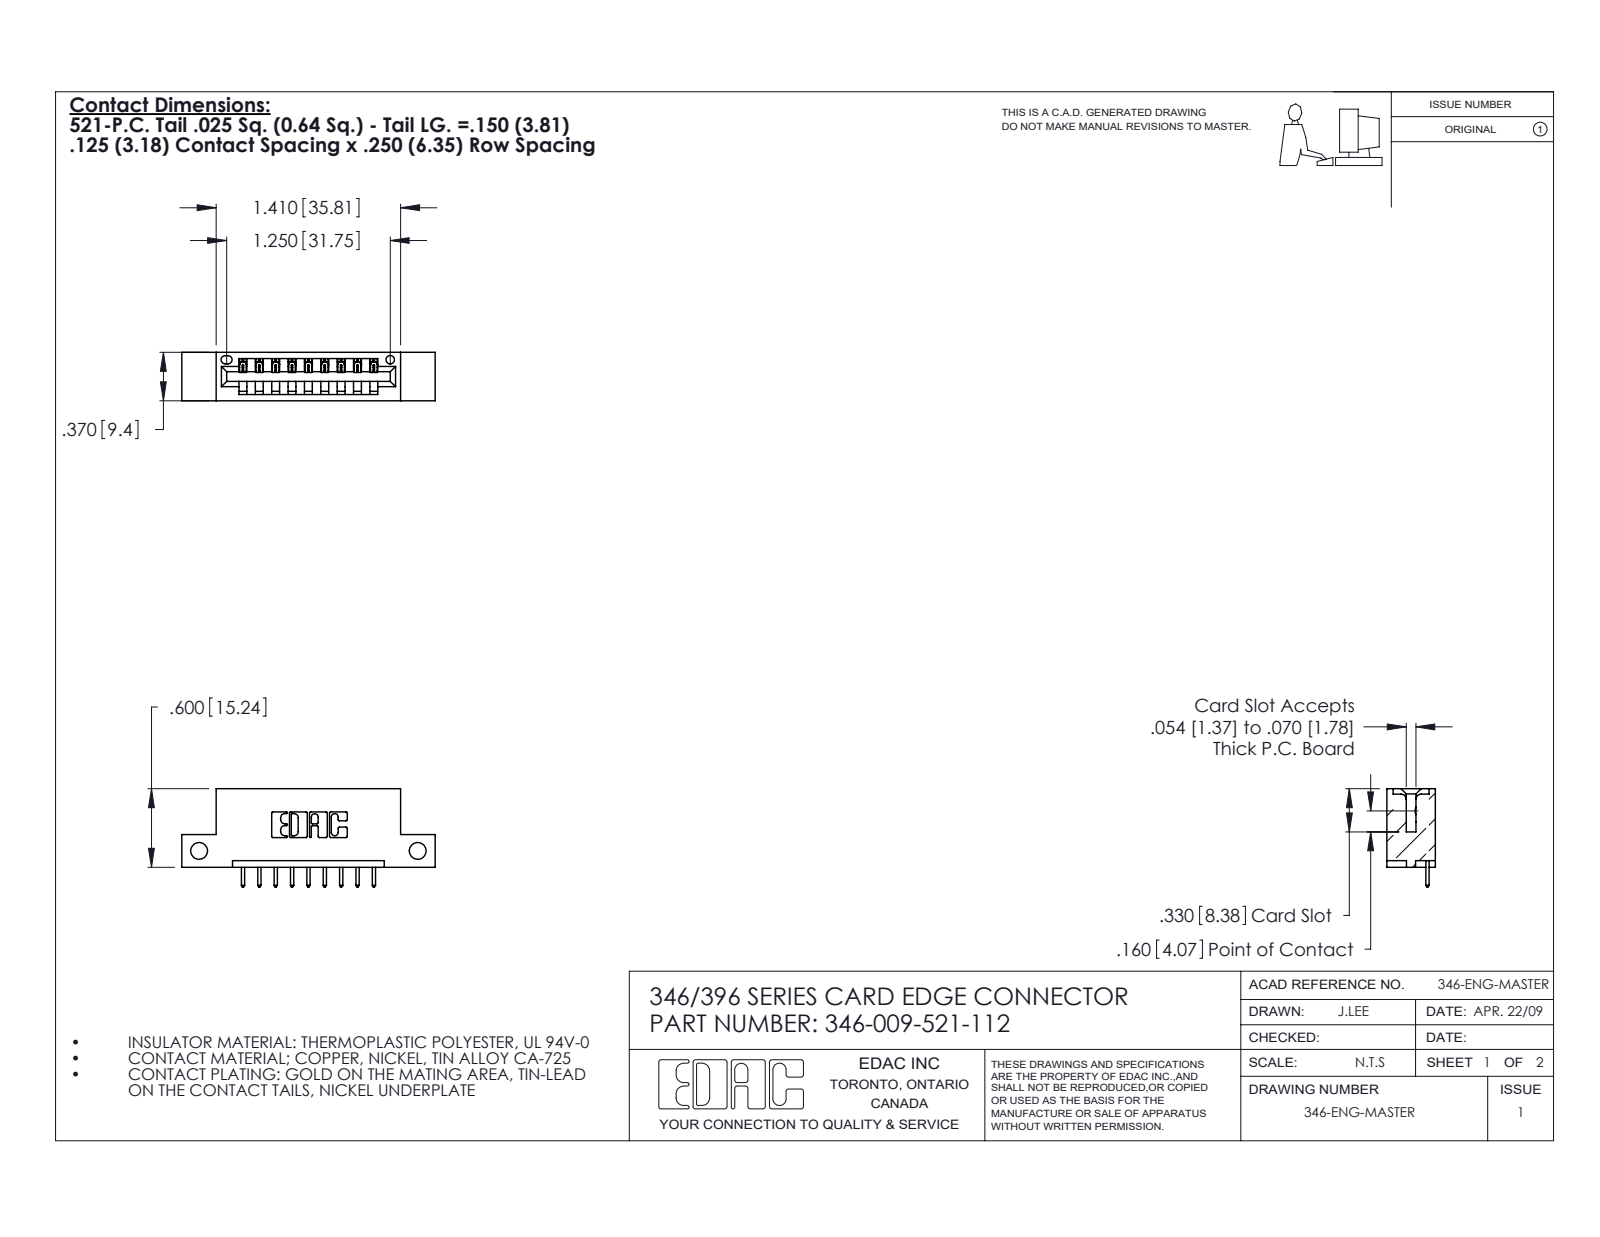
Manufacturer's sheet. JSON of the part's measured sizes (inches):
{"part_name": "346 Part_Flush Mounting Lugs - Side Mount; 346-009-521-112; 345-292-001_345-293-121", "step_written_by": "SolidWorks 2020 (CONFIG_CONTROL_DESIGN)", "units": "inches", "bodies": {"solids": 10, "faces": 644, "planar": 436, "cylindrical": 208, "other": 0}, "overall_size": [1.935, 0.75, 0.37], "volume_in3": 0.266, "surface_area_in2": 7.519, "round_holes": [[0.128, 2], [0.064, 1]], "partial_cylinders_radius": [[0.01, 22], [0.006, 18], [0.01, 18], [0.007, 6], [0.031, 6], [0.026, 3], [0.031, 2], [0.04, 2]], "face_to_face_distances": [0.25, 0.37, 0.048, 0.322, 0.148, 0.222, 0.1, 0.174, 0.072, 0.298], "hole_center_spacings": [1.67]}
